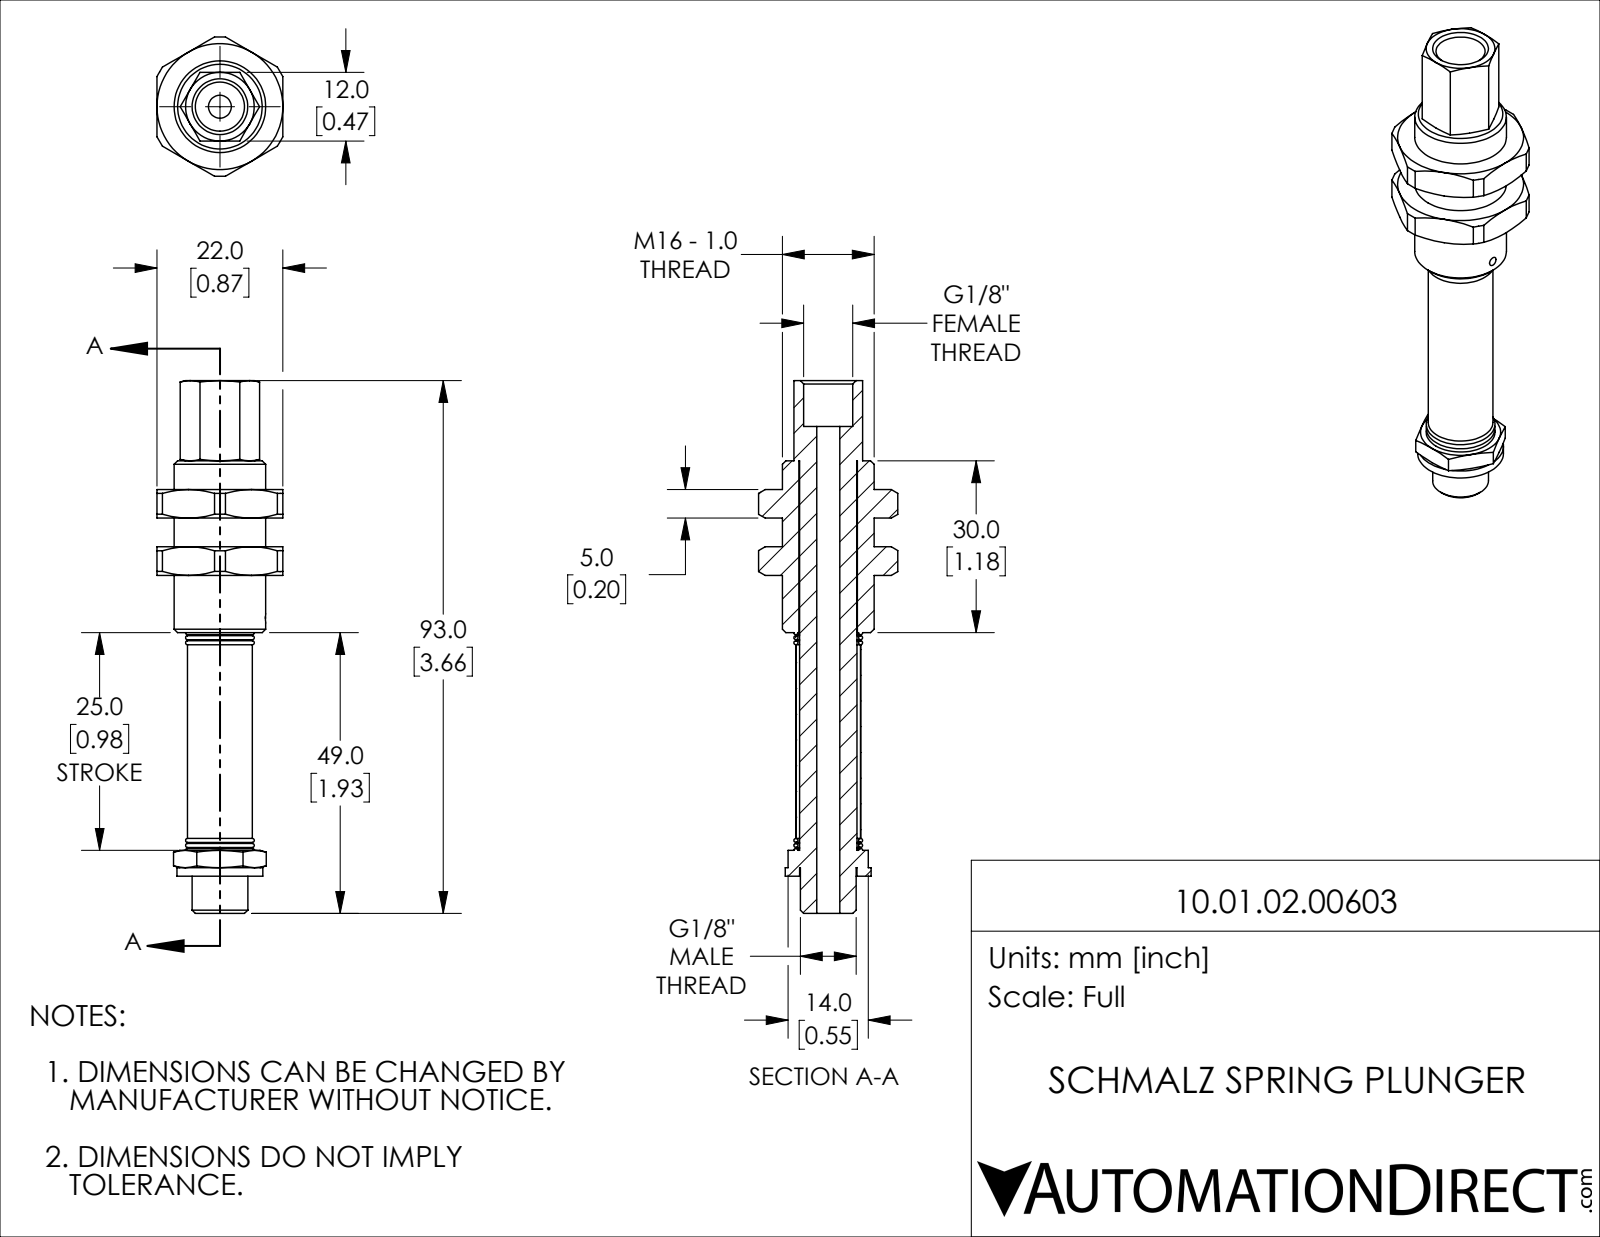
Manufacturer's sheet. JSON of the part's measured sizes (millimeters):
{"part_name": "10.01.02.00603", "step_written_by": "SolidWorks 2021 (CONFIG_CONTROL_DESIGN)", "units": "millimeters", "bodies": {"solids": 1, "faces": 188, "planar": 52, "cylindrical": 42, "other": 94}, "overall_size": [93, 24.3, 22], "volume_mm3": 12533, "surface_area_mm2": 11370, "round_holes": [[1.6, 1], [4, 1], [8.57, 1], [10, 1], [10.2, 1], [11.3, 1]], "round_bosses_or_shafts": [[16, 1], [15, 1], [11.3, 1], [9.73, 1]], "face_to_face_distances": [5, 10, 15, 12, 22, 1, 13, 20, 14, 52.5]}
